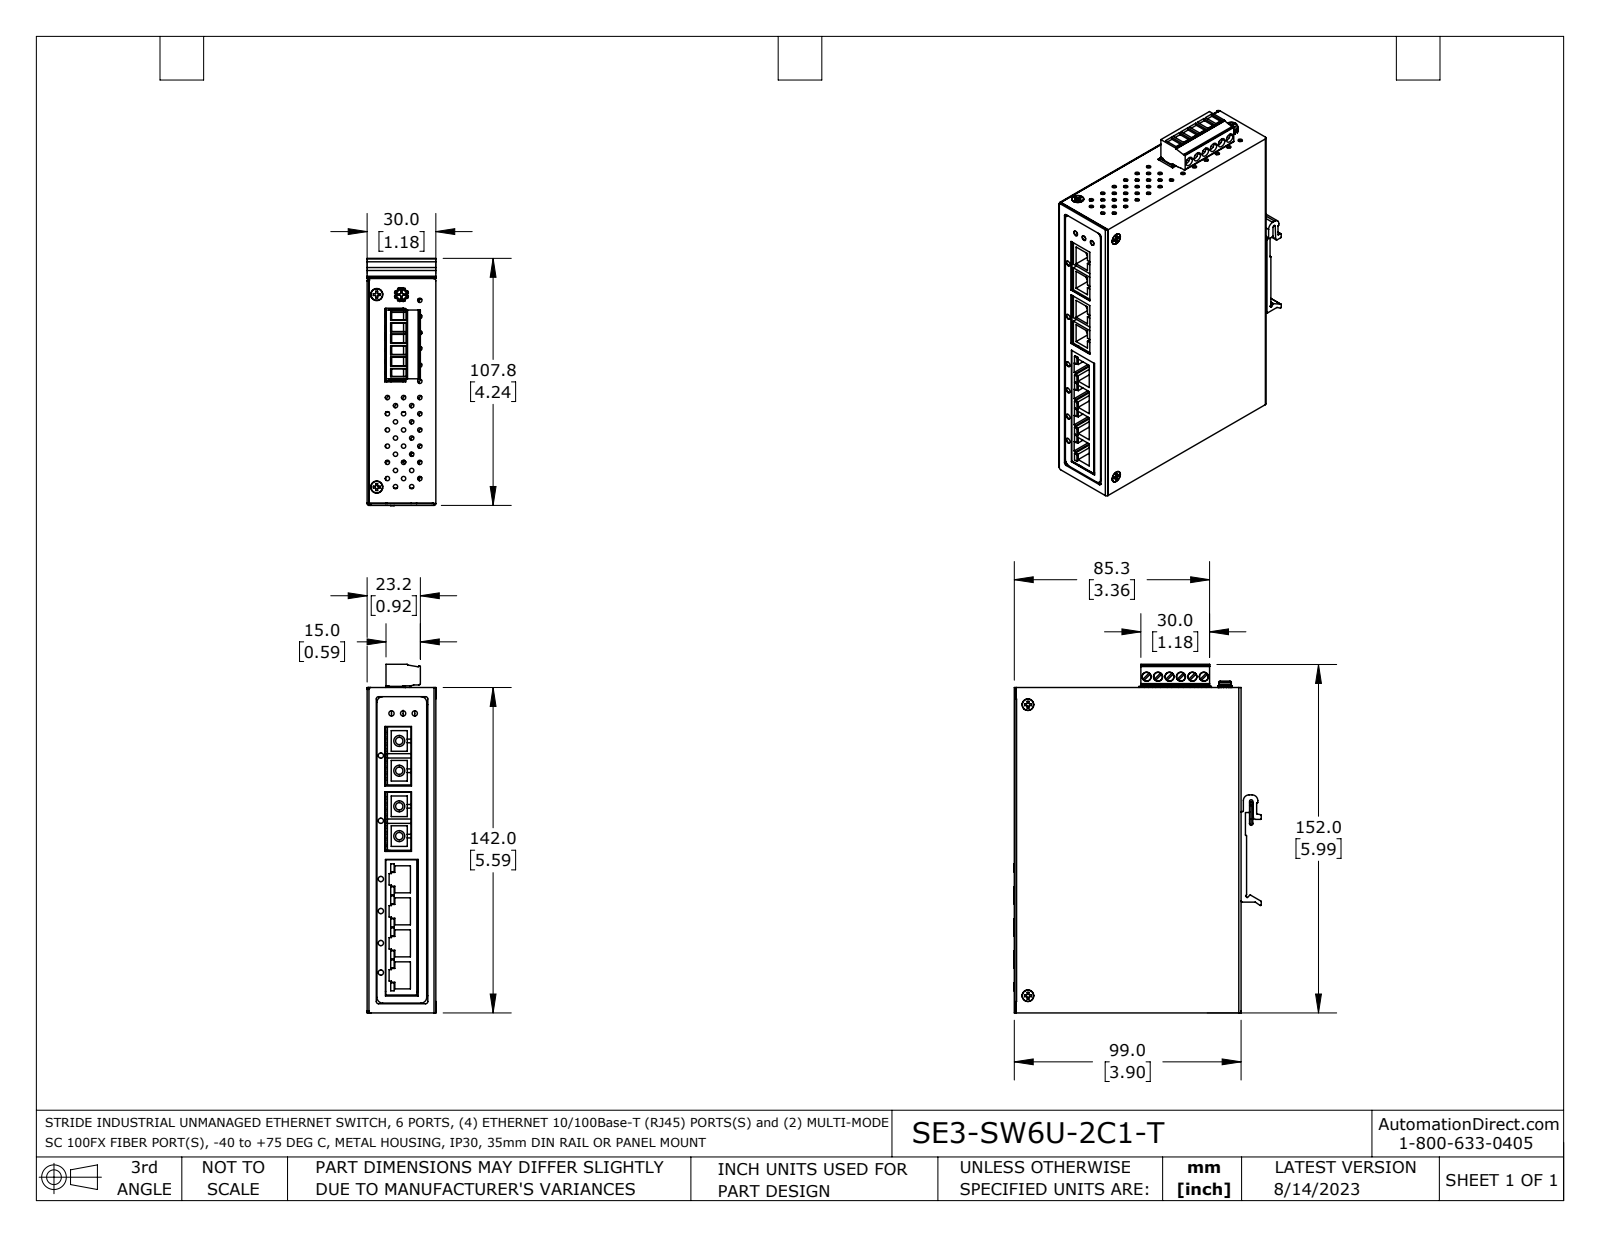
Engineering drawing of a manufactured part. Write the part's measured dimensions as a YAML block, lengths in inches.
part_name: "LEONTON_EG2-0800_3D sr1 solid but 16 bad faces1 extTB1ac coord pre CASE MOD for ET2-0602M 1aCd cmb1Cc mm coord fxt"
step_written_by: "SolidWorks 2021 (AUTOMOTIVE_DESIGN)"
units: inches
bodies: {solids: 34, faces: 2176, planar: 1065, cylindrical: 834, other: 277}
overall_size: [5.99, 4.25, 1.181]
volume: 4.542
surface_area: 180.7
round_holes:
  - {diameter: 0.075, count: 111}
  - {diameter: 0.098, count: 10}
  - {diameter: 0.091, count: 9}
  - {diameter: 0.157, count: 9}
  - {diameter: 0.097, count: 4}
  - {diameter: 0.126, count: 4}
  - {diameter: 0.118, count: 3}
  - {diameter: 0.096, count: 2}
  - {diameter: 0.096, count: 2}
  - {diameter: 0.197, count: 2}
  - {diameter: 0.209, count: 2}
  - {diameter: 0.059, count: 1}
round_bosses_or_shafts:
  - {diameter: 0.051, count: 22}
  - {diameter: 0.118, count: 13}
  - {diameter: 0.197, count: 10}
  - {diameter: 0.161, count: 8}
  - {diameter: 0.149, count: 6}
  - {diameter: 0.055, count: 6}
  - {diameter: 0.035, count: 6}
  - {diameter: 0.189, count: 4}
partial_cylinders:
  - {radius: 0.01, count: 52}
  - {radius: 0.004, count: 47}
  - {radius: 0.008, count: 17}
  - {radius: 0.012, count: 14}
  - {radius: 0.039, count: 13}
  - {radius: 0.031, count: 12}
  - {radius: 0.098, count: 7}
  - {radius: 0.115, count: 6}
face_to_face_distances: [0.031, 0.039, 1.15, 1.11, 1.142, 1.181, 5.559, 0.287, 0.823, 0.02]
hole_center_spacings: [0.44, 0.278, 0.197, 0.394, 0.557, 0.622, 0.591, 1.148]
